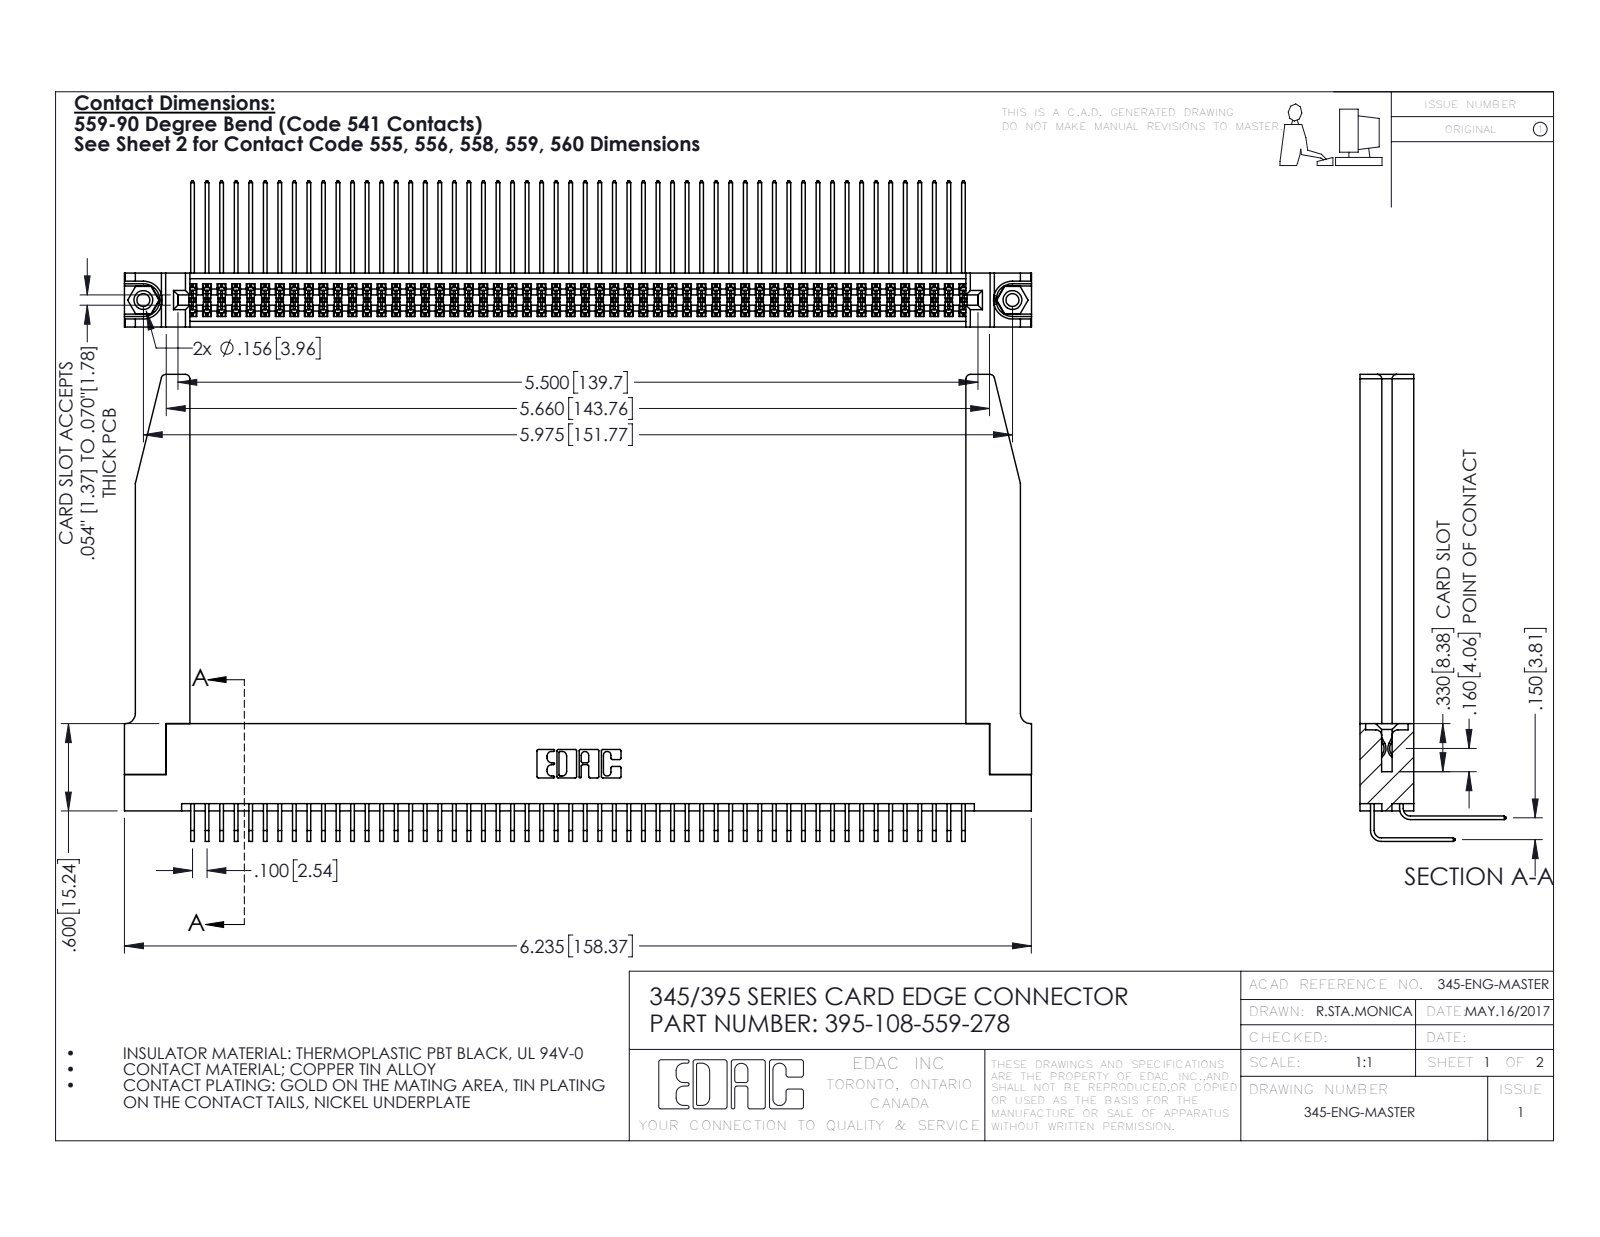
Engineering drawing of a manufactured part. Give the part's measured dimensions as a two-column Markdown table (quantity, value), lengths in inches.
| quantity | value |
| --- | --- |
| part name | 395-108-559-278; 345-292-001_558 559 Tail - 1; 345-292-001_559 Tail - 2; 345-220-078_345-220-078 (+2 more) |
| STEP written by | SolidWorks 2016 (CONFIG_CONTROL_DESIGN) |
| units | inches |
| bodies | 113 solids, 5976 faces (4002 planar, 1922 cylindrical, 52 other) |
| overall size | 6.236 × 3.209 × 1.005 |
| volume | 1.458 in³ |
| surface area | 52.44 in² |
| round holes (diameter × count) | 0.089 × 2, 0.125 × 2, 0.156 × 2, 0.064 × 1 |
| round bosses / shafts (diameter × count) | 0.155 × 2 |
| partial cylindrical surfaces (radius × count) | 0.006 × 162, 0.01 × 22, 0.03 × 8, 0.007 × 6, 0.031 × 6, 0.026 × 3, 0.014 × 2, 0.019 × 2 |
| main face-to-face distances | 0.072, 0.298, 0.37, 0.2, 0.098, 0.272, 0.025, 0.225, 0.175, 0.15 |
| hole center spacings | 0.27, 5.739, 5.975 |
